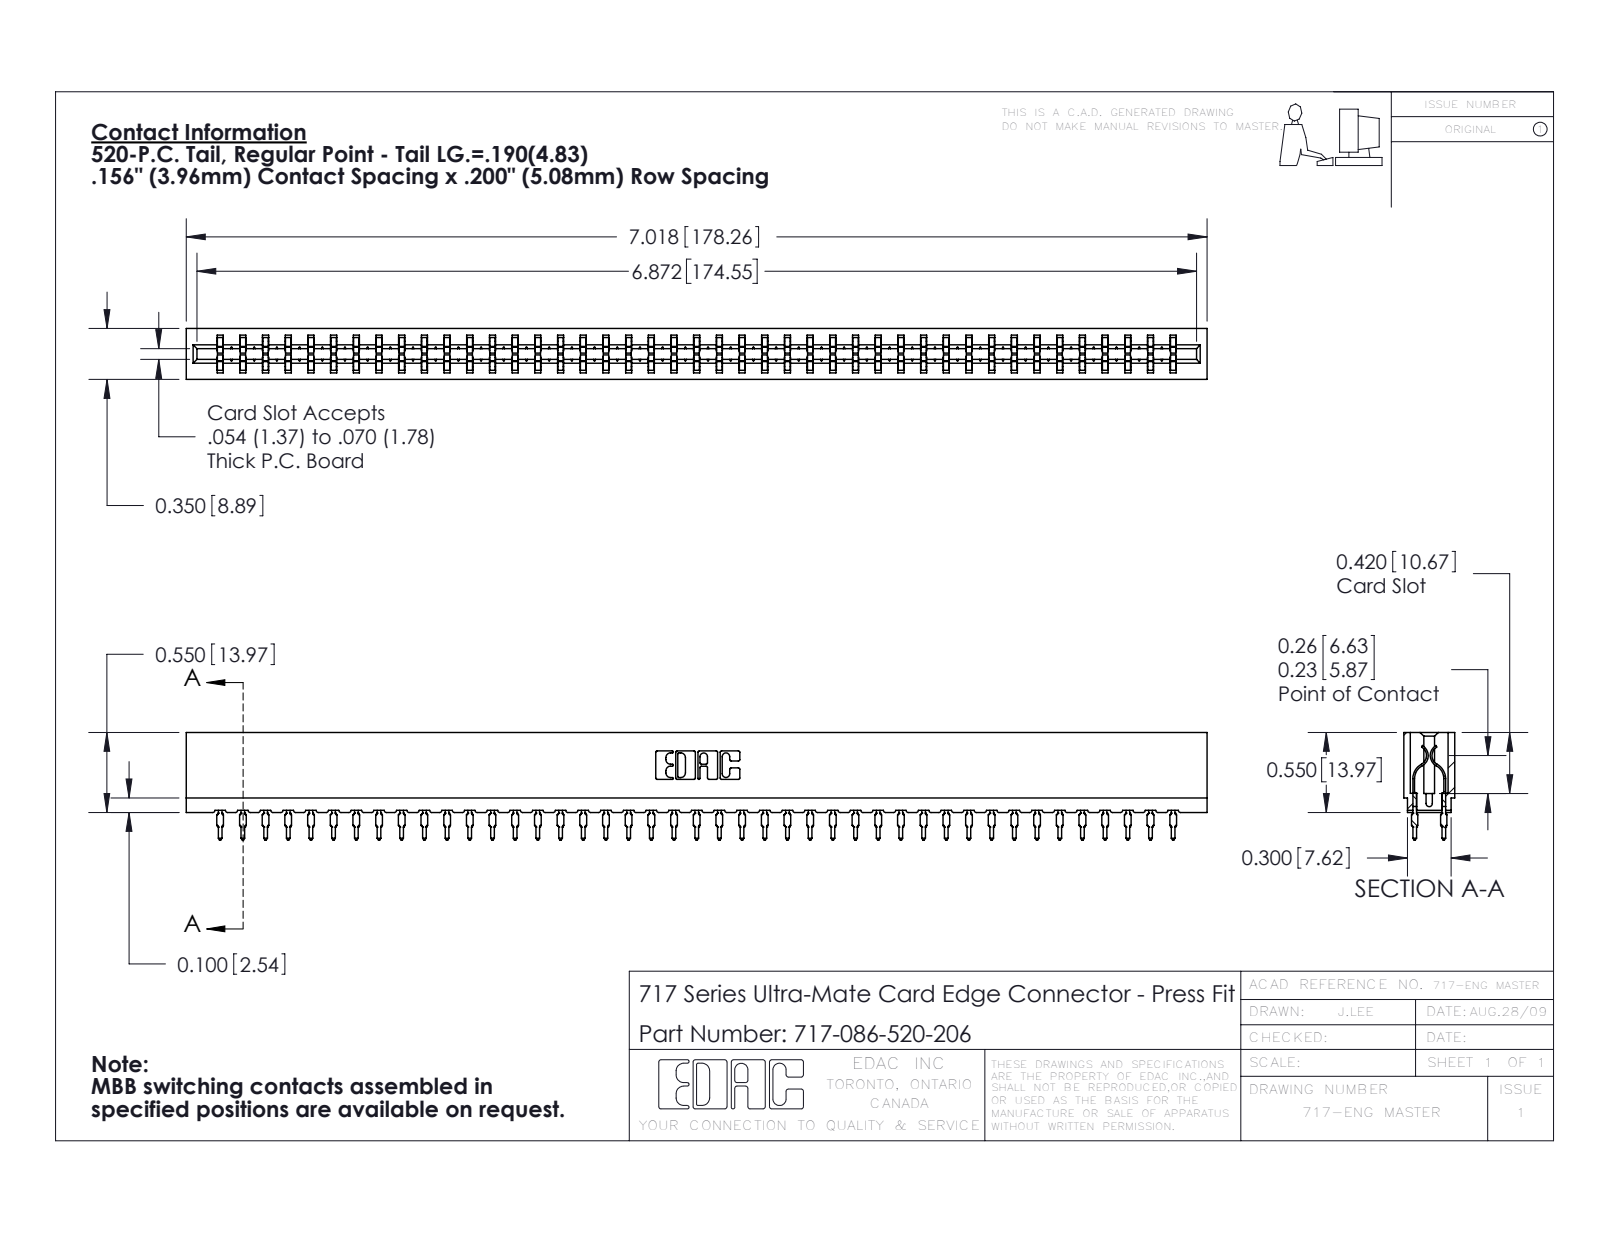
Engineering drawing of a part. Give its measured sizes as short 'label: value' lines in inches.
name: 717 Part_Insulator Option - 06; 717-086-520-206; 745-292-001_520
written by: SolidWorks 2016 (CONFIG_CONTROL_DESIGN)
unit: in
bodies: 87 solids, 7834 faces (4053 planar, 1545 cylindrical, 2236 other)
size: 7.018 × 0.739 × 0.35
volume: 0.938 in³; area: 35.79 in²
rounds: 172× R0.021, 86× R0.015, 22× R0.01, 8× R0.005, 8× R0.011, 6× R0.007, 6× R0.031, 3× R0.026
face distances: 0.212, 0.138, 0.35, 0.063, 0.287, 0.076, 0.149, 0.074, 0.045, 0.305
